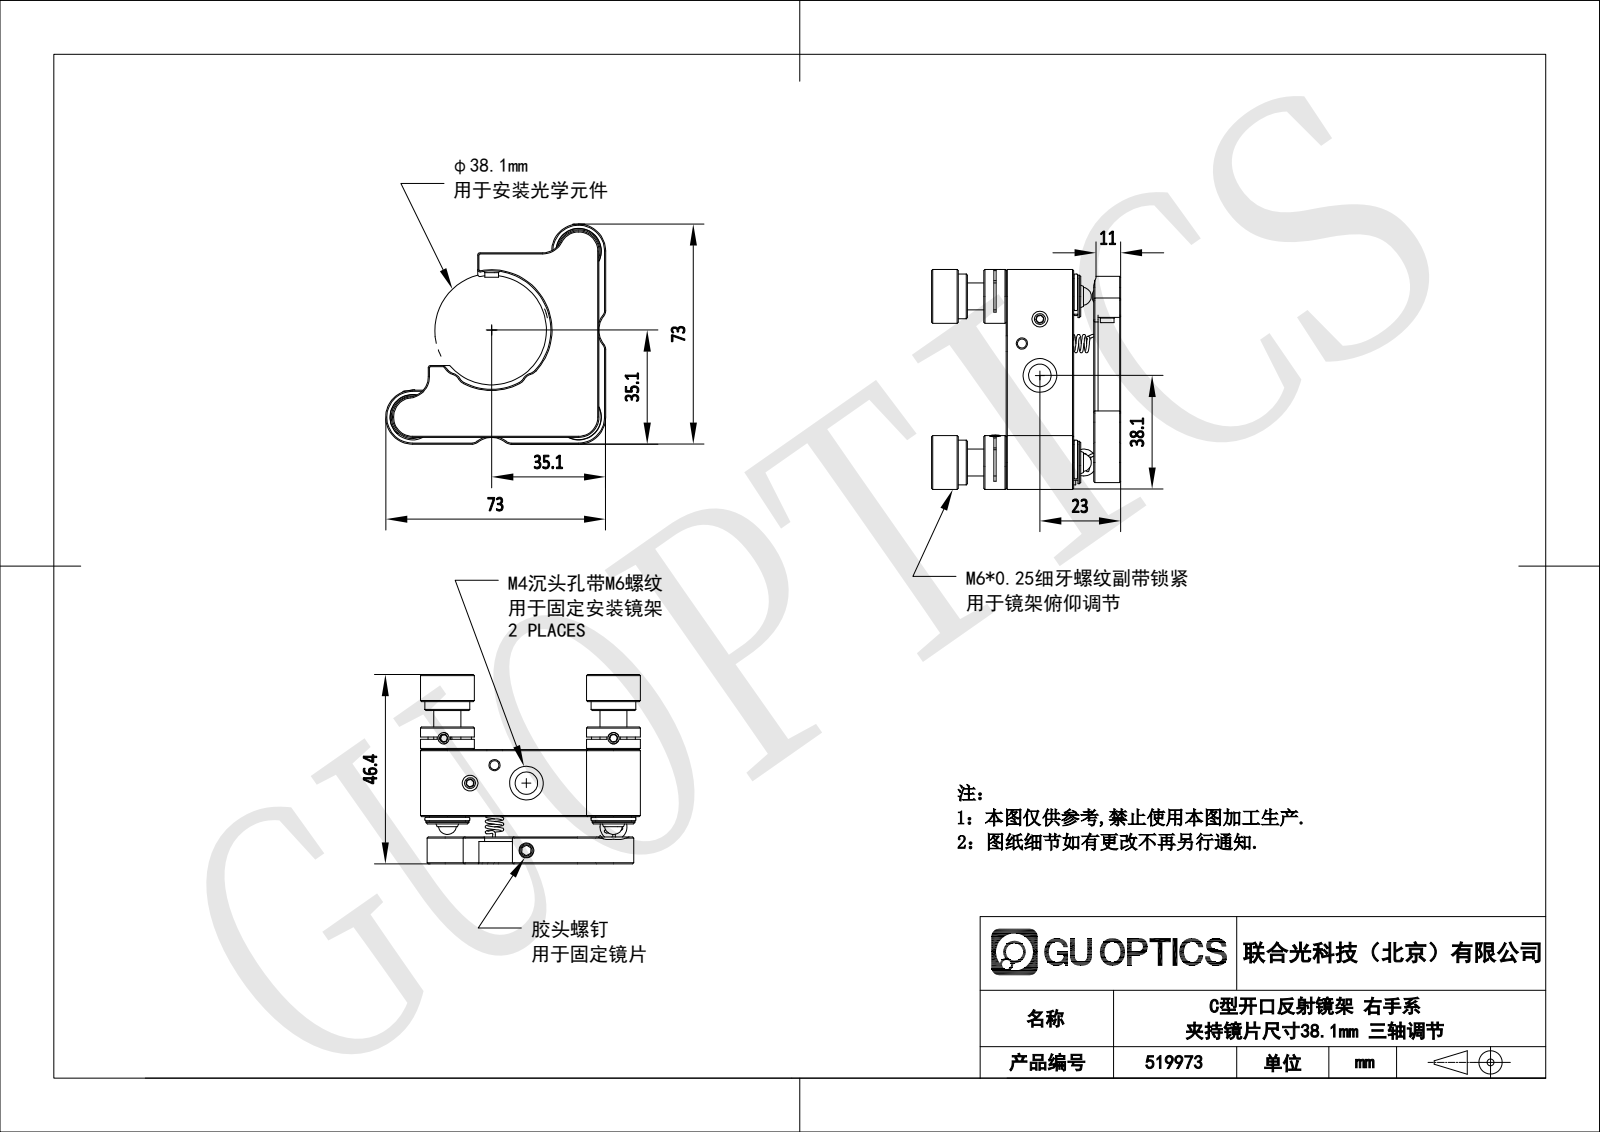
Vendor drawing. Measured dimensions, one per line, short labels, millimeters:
written by: SolidWorks 2021 (CONFIG_CONTROL_DESIGN)
unit: mm
bodies: 0 solids, 500 faces (166 planar, 157 cylindrical, 177 other)
size: 75.49 × 73.07 × 46.6
holes: 10× ⌀2.5, 5× ⌀6, 3× ⌀4, 2× ⌀5, 2× ⌀7.5, 1× ⌀3.3
bosses: 6× ⌀3, 3× ⌀12, 3× ⌀10, 3× ⌀9.5, 3× ⌀8, 2× ⌀6, 1× ⌀4
rounds: 9× R2, 5× R0.5, 4× R0.2, 3× R4.5, 2× R2.5, 2× R5, 2× R6, 2× R10
face distances: 12, 1.5, 3.5, 15.5, 30.5, 18.5, 15, 10.5, 2.25, 2.75
hole spacings: 31, 15, 24.52, 46, 10.83, 15.89, 21.59, 22.5
